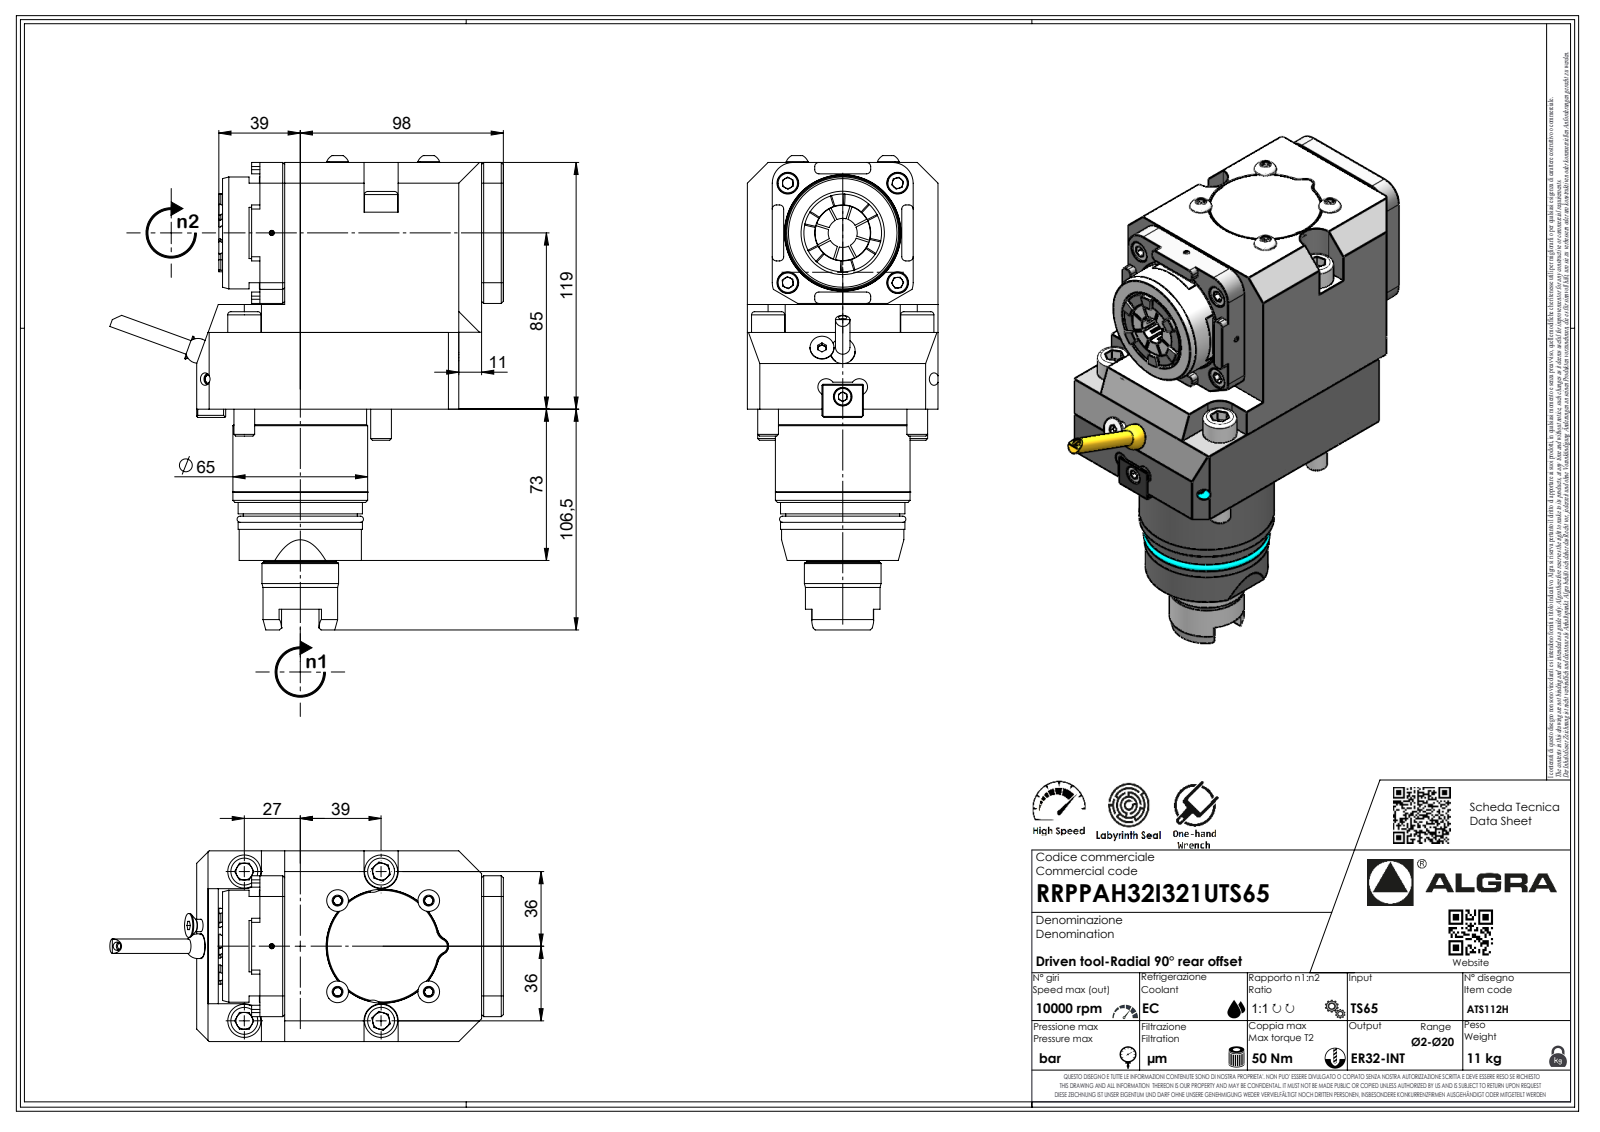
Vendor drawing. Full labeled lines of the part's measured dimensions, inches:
Part name (STEP PRODUCT): RRPPAH32I321UTS65
STEP written by: SolidWorks 2023 (AUTOMOTIVE_DESIGN)
Units: inches
Bodies: 1 solid, 574 faces (346 planar, 86 cylindrical, 142 other)
Overall size (bounding box): 9.008 × 7.496 × 3.622
Volume: 95.5 in³ · Surface area: 159.8 in²
Round holes (diameter × count): ⌀0.083 ×1, ⌀0.157 ×1
Round bosses / shafts (diameter × count): ⌀0.413 ×4, ⌀0.394 ×4, ⌀0.63 ×2, ⌀2.559 ×1, ⌀2.558 ×1, ⌀2.52 ×1, ⌀2.362 ×1, ⌀2.323 ×1
Partial cylindrical surfaces — rounded edges, fillets, slot ends (radius × count): R0.079 ×16, R0.013 ×7, R0.02 ×7, R0.146 ×7, R0.03 ×4, R0.394 ×4, R0.325 ×2, R0.008 ×1
Main face-to-face distances: 3.622, 4.685, 0.472, 0.433, 0.866, 1.988, 4.49, 5.356, 2.697, 3.15
